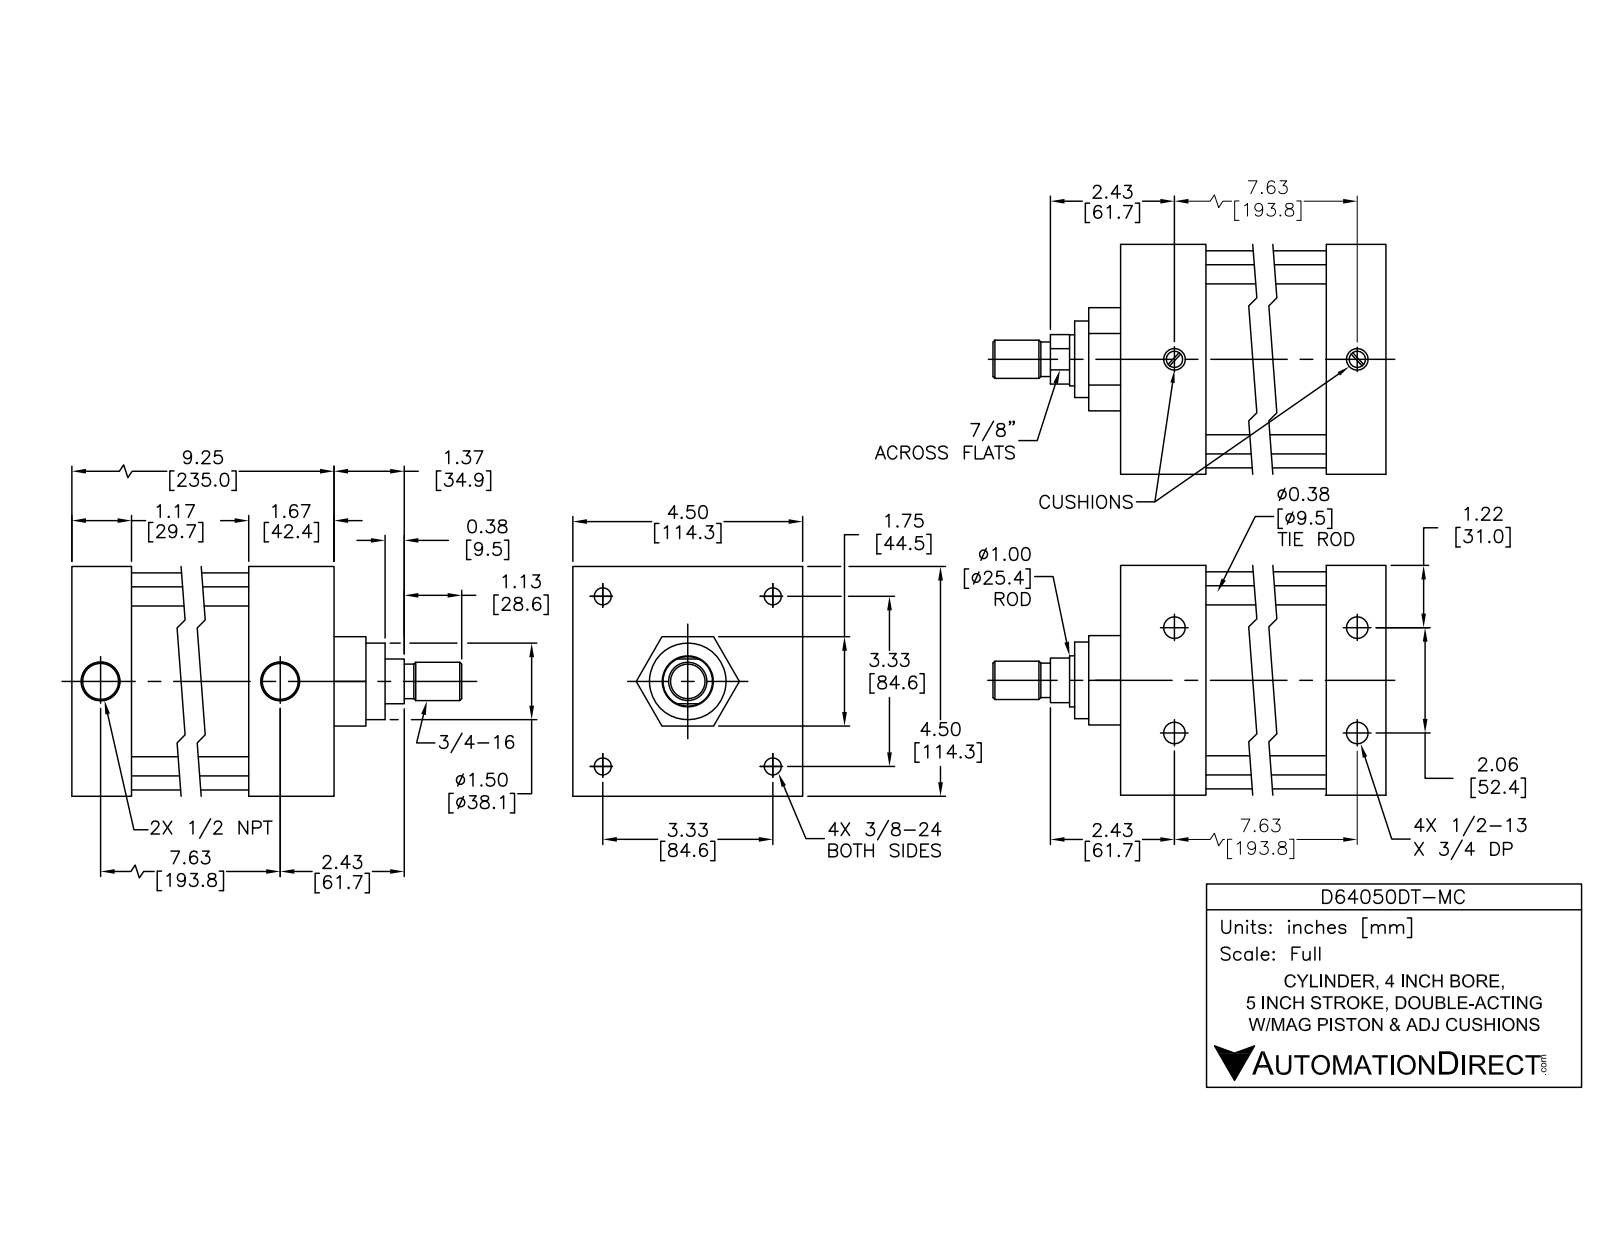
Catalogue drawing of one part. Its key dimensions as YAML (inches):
part_name: "D64050DT-M BODY; D64050DT-MC; D64050DT-M PISTON"
step_written_by: "SolidWorks 2015 (AUTOMOTIVE_DESIGN)"
units: inches
bodies: {solids: 12, faces: 303, planar: 99, cylindrical: 114, other: 90}
overall_size: [11.745, 4.5, 4.5]
volume: 91.16
surface_area: 457
round_holes:
  - {diameter: 0.33, count: 4}
  - {diameter: 0.406, count: 4}
  - {diameter: 0.417, count: 4}
  - {diameter: 0.625, count: 4}
  - {diameter: 0.5, count: 2}
  - {diameter: 0.766, count: 2}
  - {diameter: 1, count: 1}
  - {diameter: 1.003, count: 1}
  - {diameter: 4, count: 1}
round_bosses_or_shafts:
  - {diameter: 0.609, count: 4}
  - {diameter: 0.375, count: 4}
  - {diameter: 0.34, count: 4}
  - {diameter: 4.25, count: 1}
  - {diameter: 3.997, count: 1}
  - {diameter: 1.75, count: 1}
  - {diameter: 0.997, count: 1}
  - {diameter: 0.97, count: 1}
partial_cylinders:
  - {radius: 0.45, count: 4}
face_to_face_distances: [4.5, 0.08, 6.326, 9.246, 1.75, 7.997, 1.249, 6.751, 1.246, 2.495]
hole_center_spacings: [1.031, 2.349, 3.322, 7.691, 7.622, 2.062, 4.698, 7.896]
